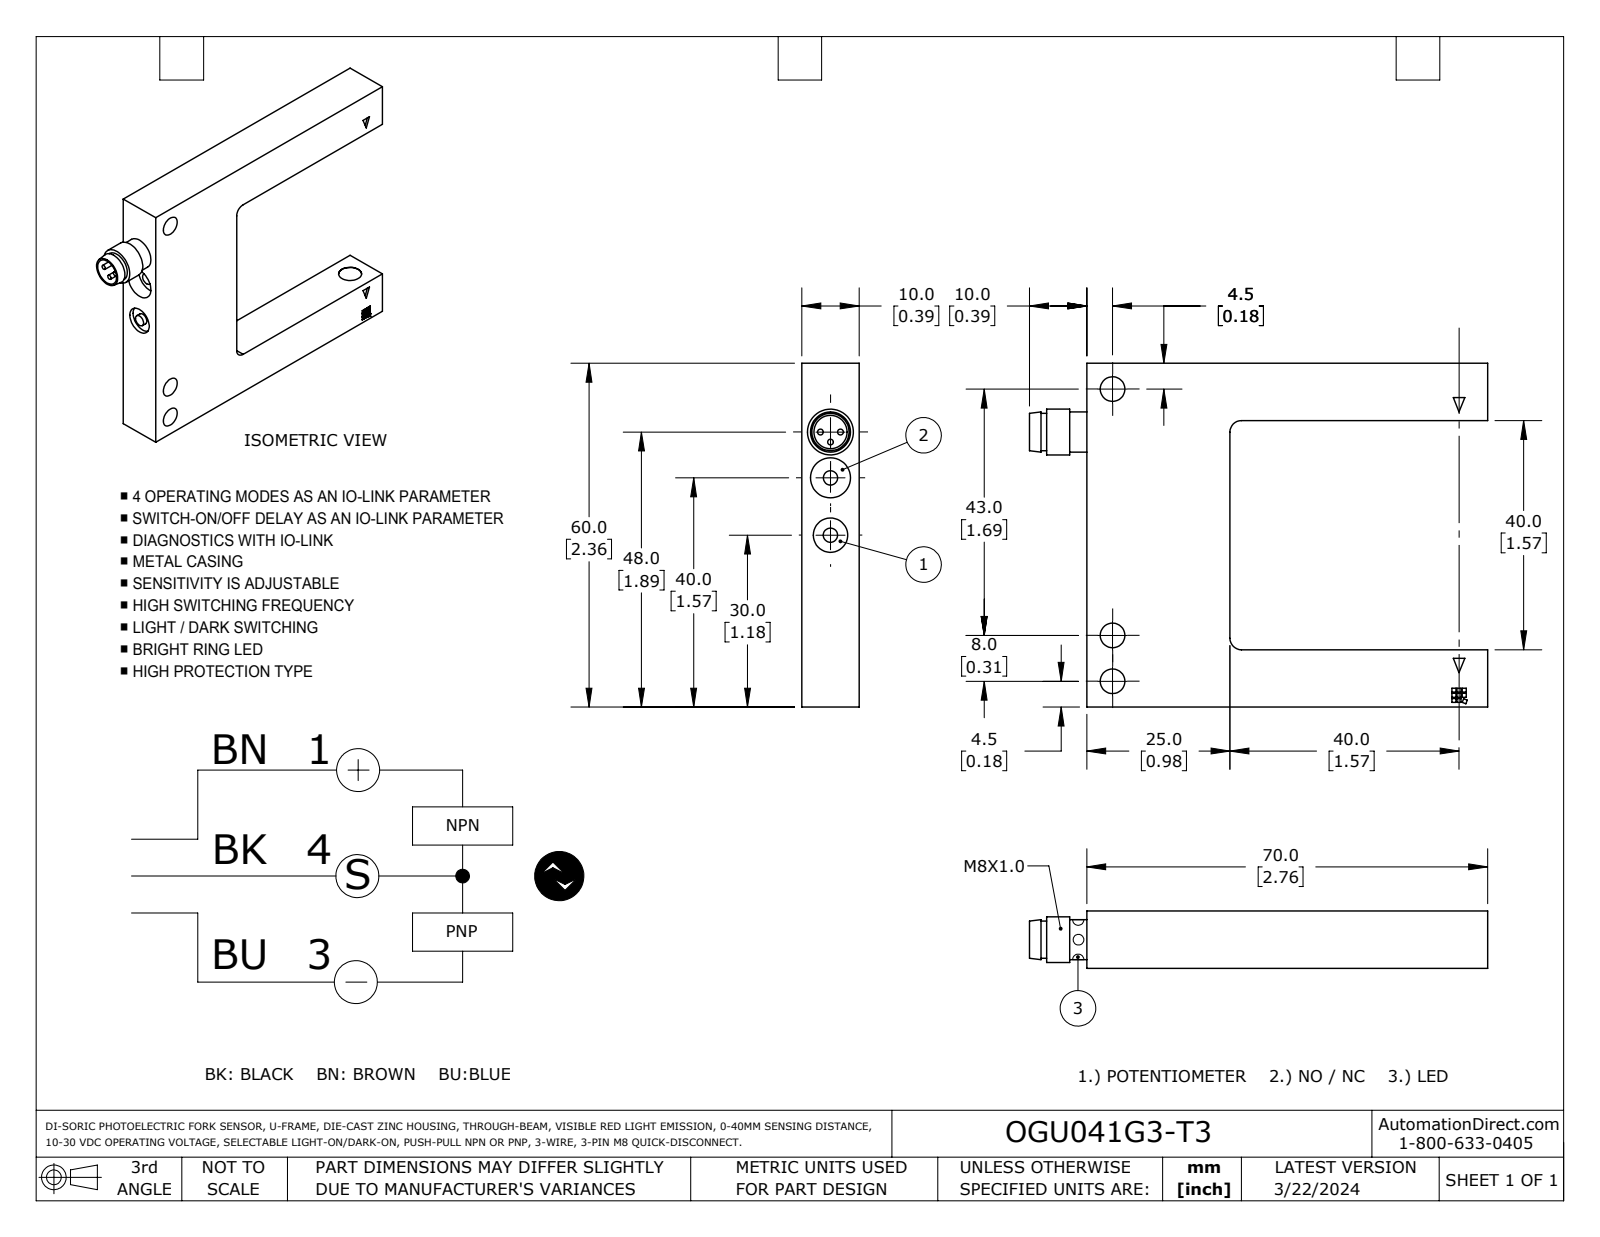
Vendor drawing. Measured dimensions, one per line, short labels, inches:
name: OGU041G3-T3
written by: SolidWorks 2023 (AUTOMOTIVE_DESIGN)
unit: in
bodies: 1 solid, 112 faces (91 planar, 20 cylindrical, 1 other)
size: 3.15 × 2.362 × 0.394
volume: 1.448 in³; area: 14.18 in²
holes: 3× ⌀0.169, 1× ⌀0.118, 1× ⌀0.197, 1× ⌀0.228, 1× ⌀0.236, 1× ⌀0.276
bosses: 3× ⌀0.039, 2× ⌀0.098, 1× ⌀0.315, 1× ⌀0.276, 1× ⌀0.256
rounds: 3× R0.079
face distances: 0.394, 1.969, 2.362, 1.575, 0.984, 2.756, 1.772, 0.392, 0.039, 1.97
hole spacings: 0.315, 0.394, 0.709, 1.693, 2.008
